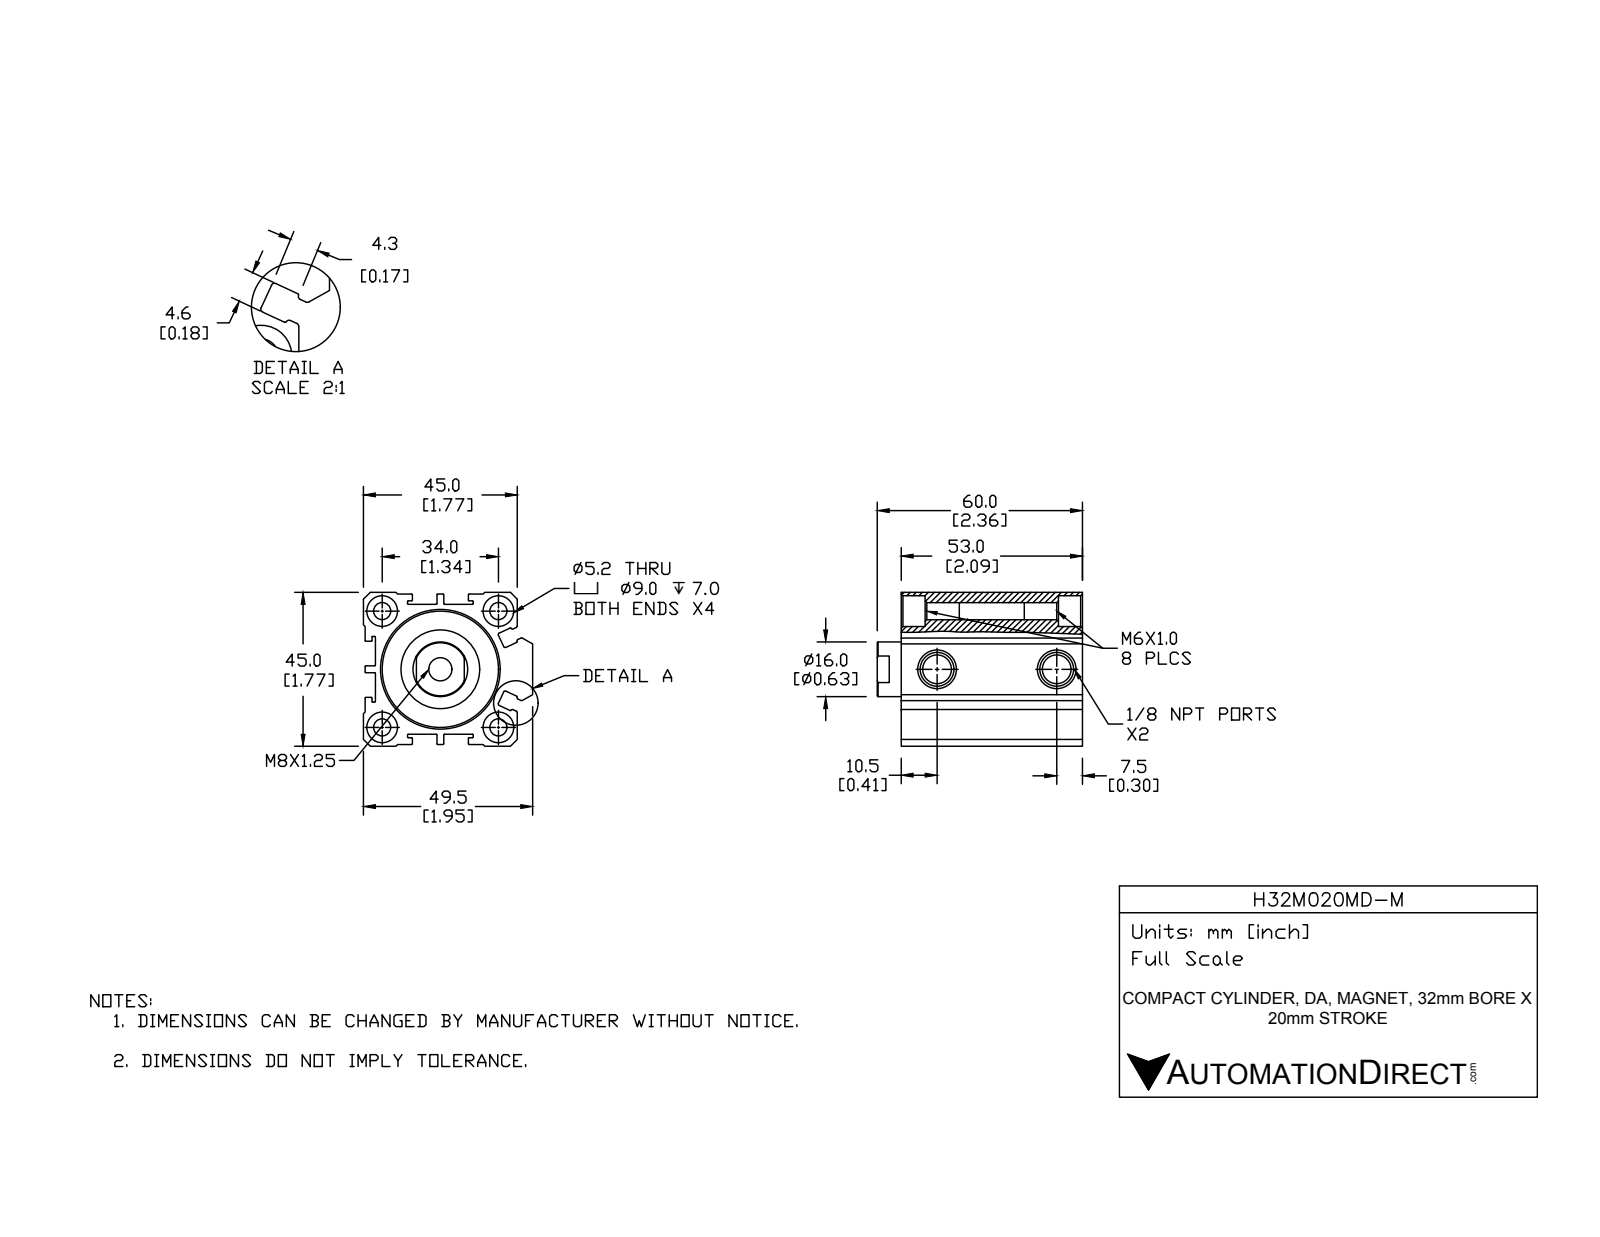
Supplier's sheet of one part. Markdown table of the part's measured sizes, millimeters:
| quantity | value |
| --- | --- |
| part name | H32M020MD-M; H32M020MD-M-PISTON; H32M020MD-M-BODY |
| STEP written by | SolidWorks 2015 (CONFIG_CONTROL_DESIGN) |
| units | millimeters |
| bodies | 2 solids, 255 faces (99 planar, 103 cylindrical, 53 other) |
| overall size | 60 × 49.5 × 45 |
| volume | 76 742 mm³ |
| surface area | 33 422 mm² |
| round holes (diameter × count) | 5 × 4, 9 × 4, 8.43 × 2, 6.8 × 1, 16 × 1, 23 × 1, 28 × 1, 32 × 1, 34 × 1 |
| round bosses / shafts (diameter × count) | 20 × 1 |
| partial cylindrical surfaces (radius × count) | 0.2 × 40, 0.5 × 12 |
| main face-to-face distances | 41.5, 3.5, 3, 44.5, 45, 0.5, 41, 4.5, 38, 42.5 |
| hole center spacings | 24.04, 34, 48.08, 35 |
